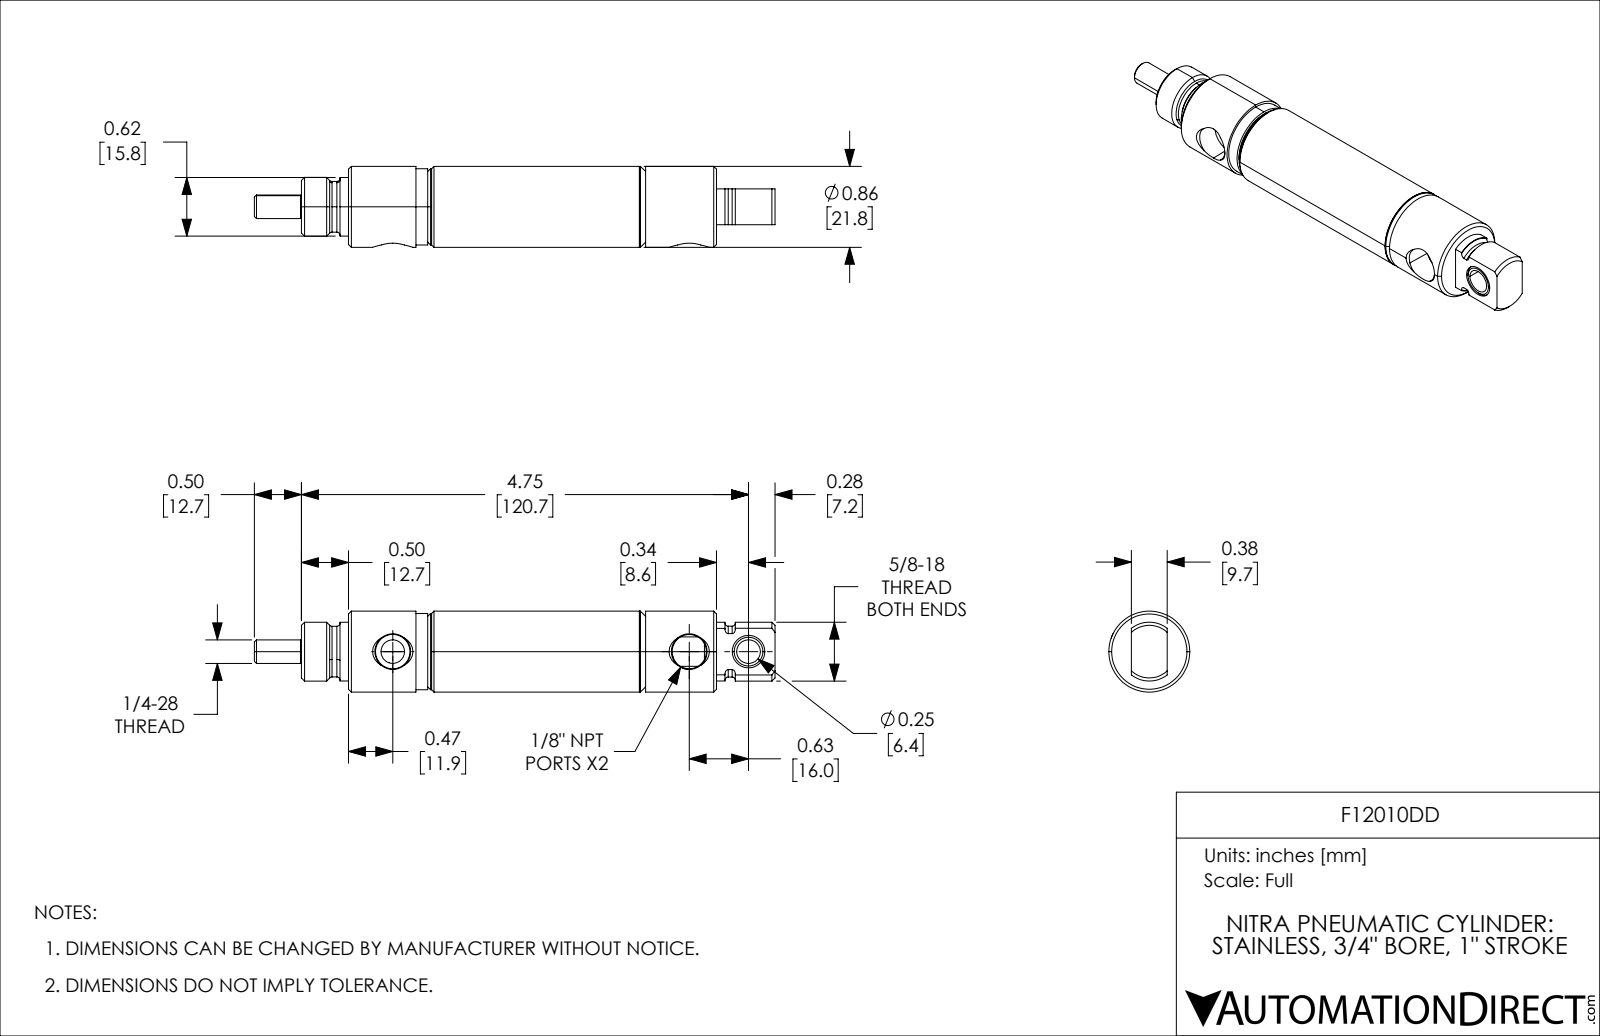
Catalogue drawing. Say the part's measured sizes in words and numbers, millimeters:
The part is named "F12010DD_3; F12010DD_5; F12010DD_7; F12010DD_9 (+2 more)". Its 3-D file was written by "SolidWorks 2021 (CONFIG_CONTROL_DESIGN)". It is 5 solids with 158 faces: 29 planar, 61 cylindrical and 68 other. Overall it measures 140.51 by 21.84 by 21.84 millimeters. Its volume is 32 136 cubic millimeters and its surface area 20 230 square millimeters. Round holes: 1 of diameter 6.35, 1 of diameter 6.38, 1 of diameter 6.95, 1 of diameter 7.92, 1 of diameter 8.78, 1 of diameter 9.23, 1 of diameter 12.7, 1 of diameter 17.83. Round bosses or shafts: 1 of diameter 21.84, 1 of diameter 20.57, 1 of diameter 19.35, 1 of diameter 15.88, 1 of diameter 15.81, 1 of diameter 13.68, 1 of diameter 6.35, 1 of diameter 5.84. Partial cylindrical surfaces (rounded edges, fillets, slot ends): 1 of radius 6.84. The main face-to-face distances are 21.43, 40.49, 87.32, 25.4, 46.83, 71.52, 46.12, 24.69, 53.19, 12.7. The hole center spacings are 16, 80.01, 96.01.
